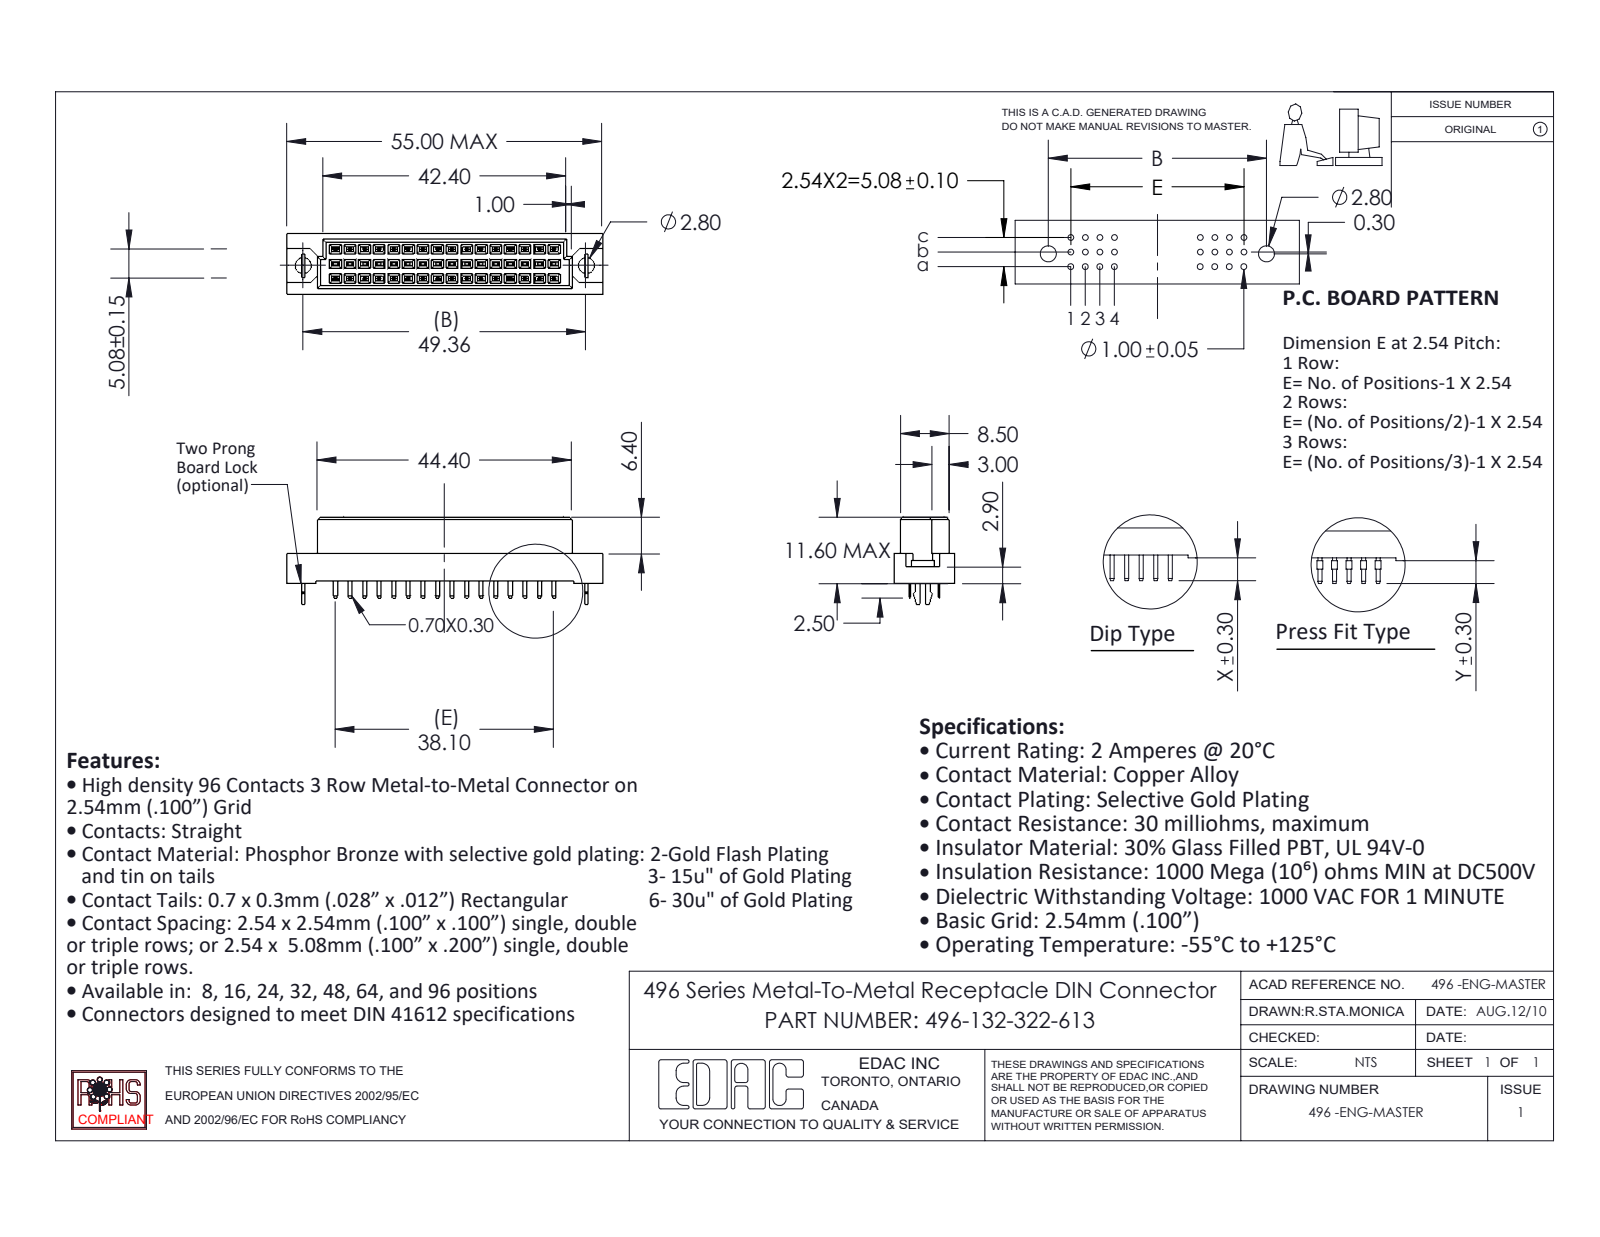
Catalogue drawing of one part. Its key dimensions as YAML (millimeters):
part_name: "496-290_22; 496 Part_48; 496 Bore-lock; 496-132-322-613"
step_written_by: "SolidWorks 2020 (CONFIG_CONTROL_DESIGN)"
units: millimeters
bodies: {solids: 35, faces: 1022, planar: 1016, cylindrical: 6, other: 0}
overall_size: [55, 15.2, 10.6]
volume: 4657
surface_area: 4766
round_holes:
  - {diameter: 2.8, count: 2}
partial_cylinders:
  - {radius: 0.53, count: 1}
face_to_face_distances: [2.54, 5.08, 1.05, 9.55, 0.81, 0.56, 0.55, 10.6, 3.35, 1.73]
hole_center_spacings: [49.36]
